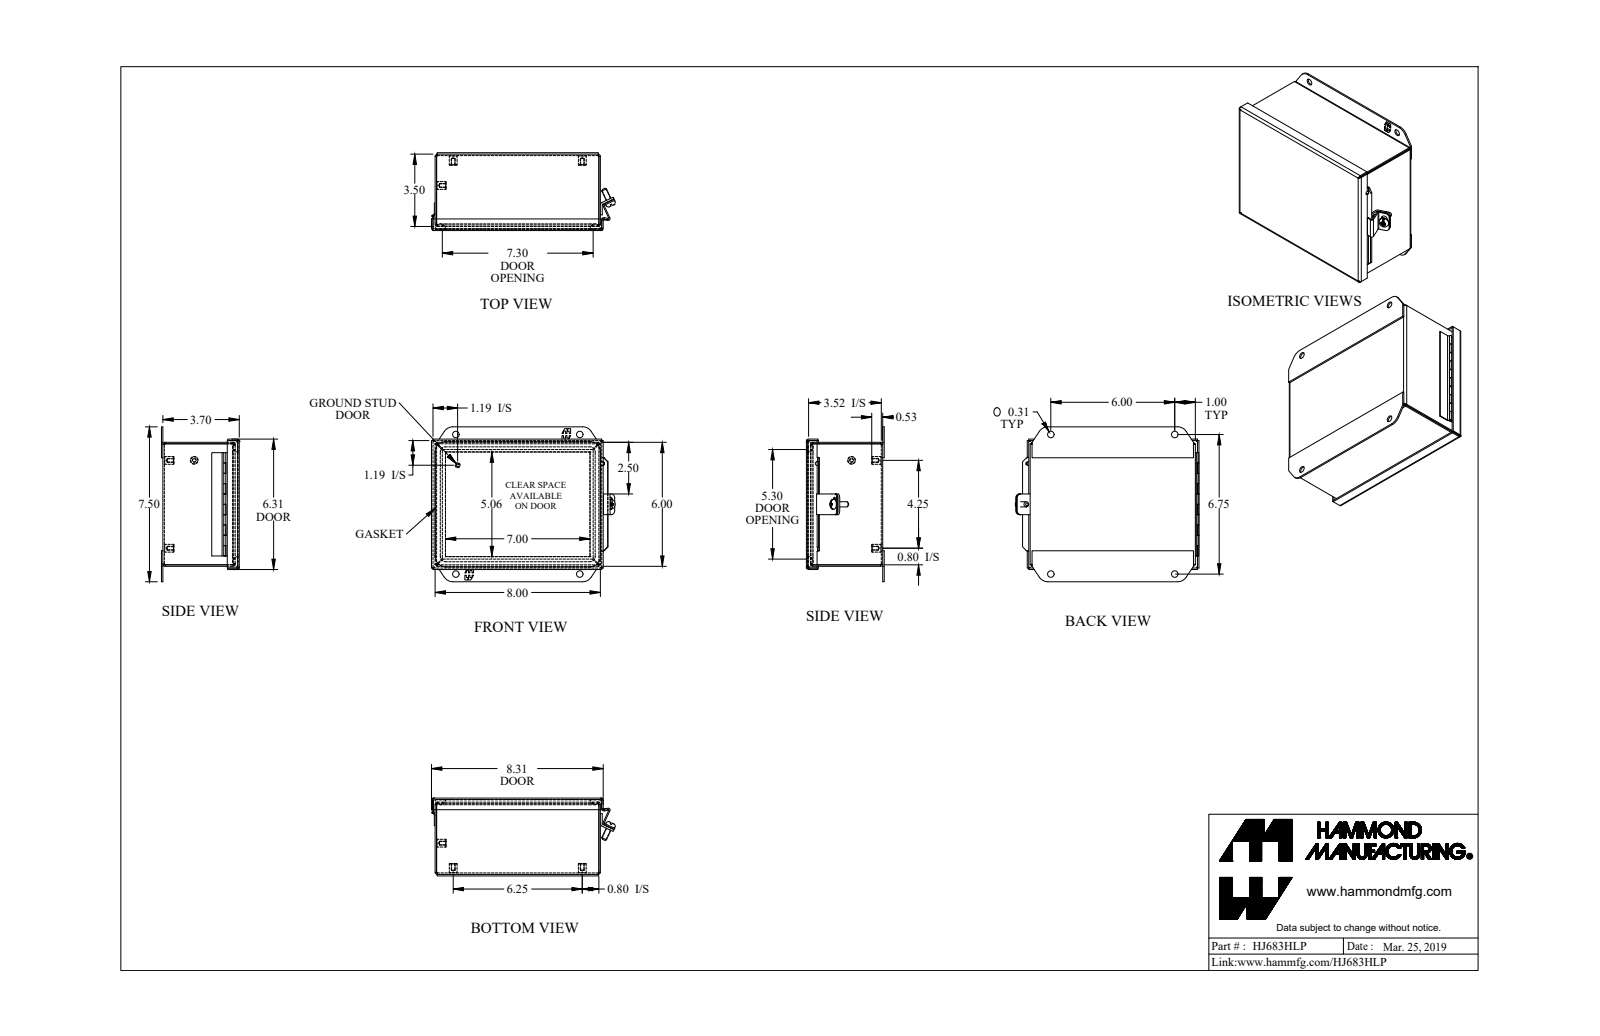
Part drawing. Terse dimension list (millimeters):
name: HJ683HLP
written by: SolidWorks 2018 (AUTOMOTIVE_DESIGN)
unit: mm
bodies: 17 solids, 574 faces (307 planar, 165 cylindrical, 102 other)
size: 226 × 190.5 × 95.7
volume: 332 200 mm³; area: 367 200 mm²
holes: 5× ⌀4, 4× ⌀8, 1× ⌀1.3, 1× ⌀5.4
bosses: 5× ⌀9.5, 2× ⌀6.4, 1× ⌀12.2, 1× ⌀4.8, 1× ⌀2.5, 1× ⌀1.1
rounds: 16× R6.4, 13× R0.9, 13× R2.7, 4× R12.7, 4× R12.7, 2× R0.3, 2× R0.7, 2× R2.2
face distances: 1.8, 92.1, 93.9, 150.6, 90.2, 201.4, 152.4, 148.7, 3.7, 95.7
hole spacings: 31.9, 31.9, 108, 139.7, 139.8, 152.4, 158.8, 158.8
